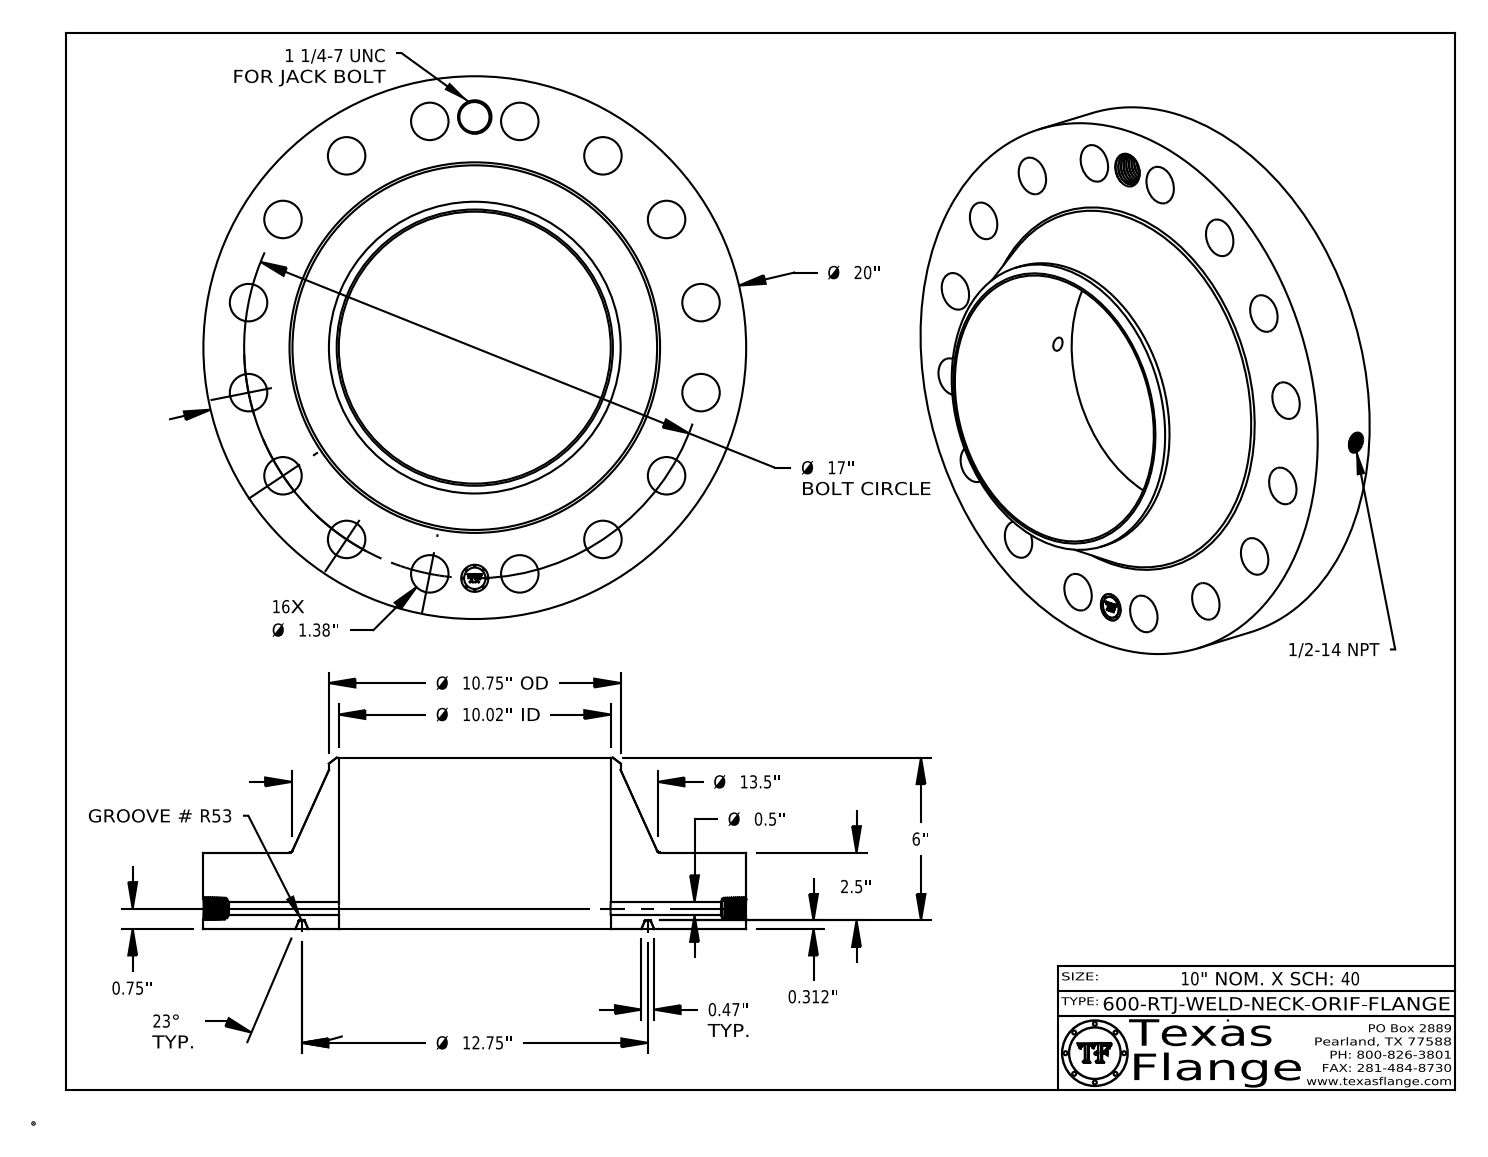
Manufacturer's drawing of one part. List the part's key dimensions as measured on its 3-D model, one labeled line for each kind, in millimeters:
Part name (STEP PRODUCT): 600-RTJ-WELD-NECK
STEP written by: CATIA V5 STEP AP214 (AUTOMOTIVE_DESIGN)
Units: millimetres
Bodies: 1 solid, 822 faces (370 planar, 117 cylindrical, 335 other)
Overall size (bounding box): 508 × 508 × 160.3
Volume: 11 510 000 mm³ · Surface area: 725 800 mm²
Round holes (diameter × count): ⌀35.1 ×16, ⌀12.7 ×1, ⌀17.1 ×1, ⌀25.4 ×1, ⌀28.2 ×1, ⌀254.5 ×1
Round bosses / shafts (diameter × count): ⌀1.5 ×8, ⌀508 ×1, ⌀273.1 ×1, ⌀20 ×1
Main face-to-face distances: 71.4, 7.9, 63.5, 160.3, 152.4, 88.9, 71, 63.1, 0.4, 89.3
Hole centre spacings: 215.9, 305.3, 398.9, 423.5, 84.3, 239.9, 359, 431.8
